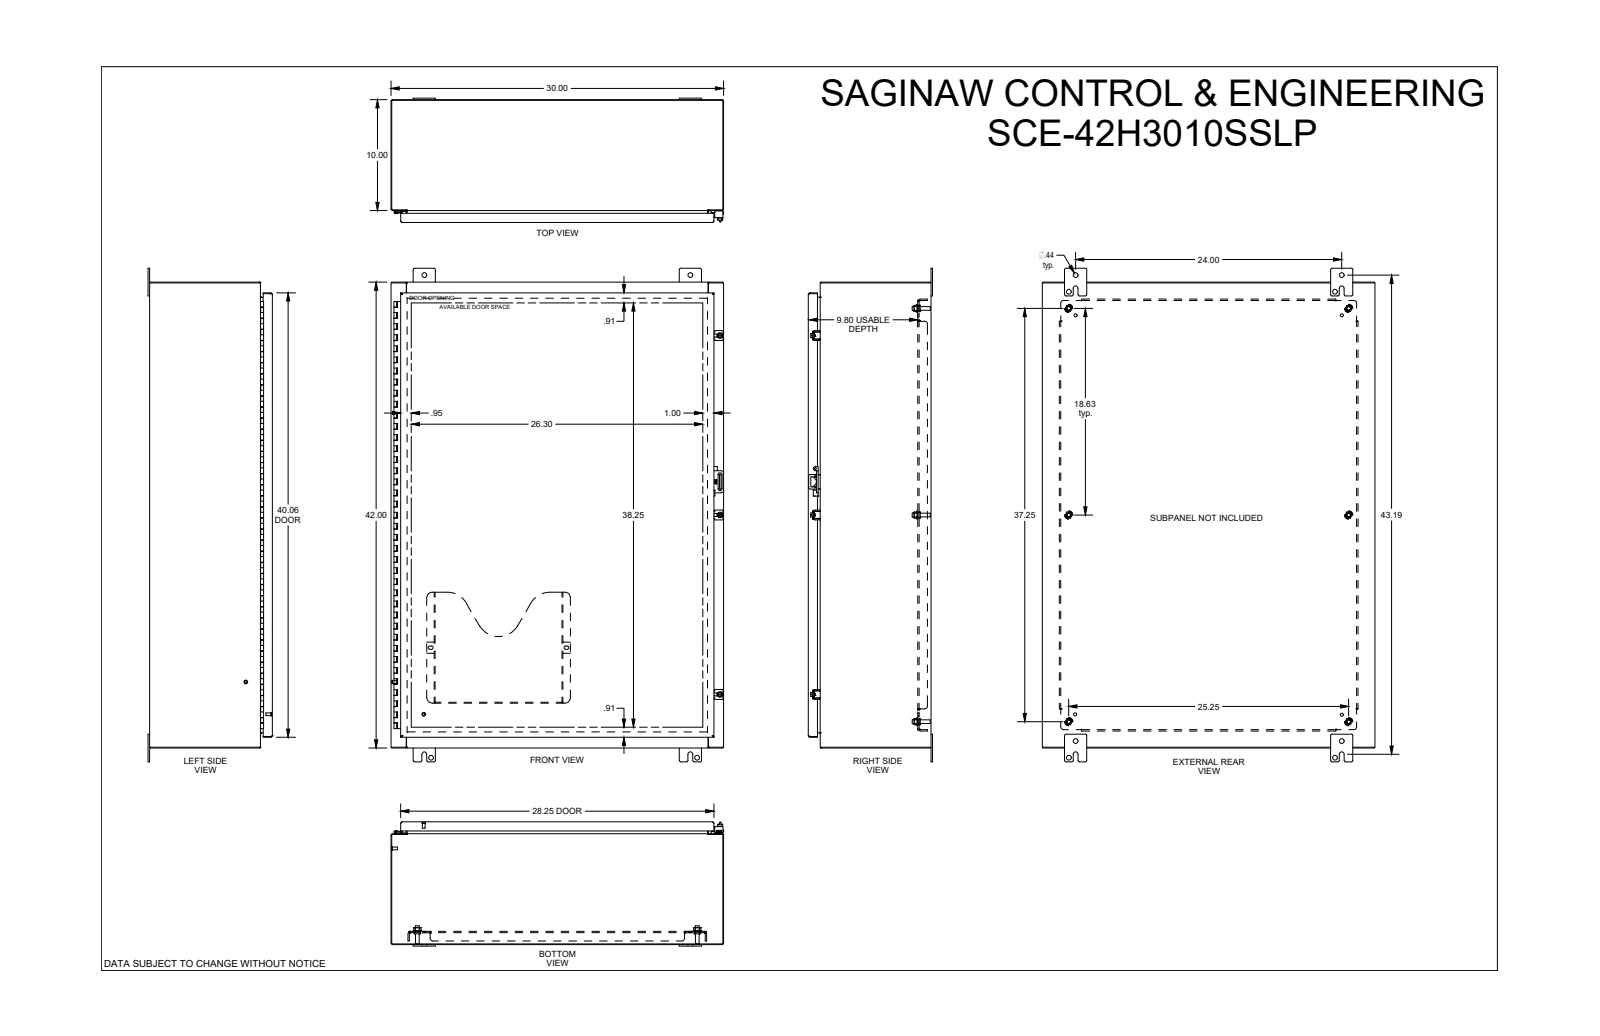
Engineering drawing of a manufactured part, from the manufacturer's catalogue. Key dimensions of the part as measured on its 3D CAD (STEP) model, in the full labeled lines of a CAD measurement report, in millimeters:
Part name (STEP PRODUCT): SCE-42H3010SSLP
STEP written by: SolidWorks 2019 (CONFIG_CONTROL_DESIGN)
Units: millimetres
Bodies: 0 solids, 4158 faces (1720 planar, 880 cylindrical, 1558 other)
Overall size (bounding box): 1130.3 × 762 × 284.7
Round holes (diameter × count): ⌀11.1 ×8, ⌀4.8 ×6, ⌀4.9 ×6, ⌀6.4 ×6, ⌀9.3 ×6, ⌀12.7 ×6, ⌀7.1 ×4, ⌀5.2 ×3, ⌀4.1 ×2, ⌀3.3 ×1, ⌀3.4 ×1
Round bosses / shafts (diameter × count): ⌀6.3 ×8, ⌀14.3 ×6, ⌀9.3 ×6, ⌀8.4 ×6, ⌀6.5 ×6, ⌀4.8 ×6, ⌀6.4 ×4, ⌀12.9 ×3
Partial cylindrical surfaces — rounded edges, fillets, slot ends (radius × count): R0.3 ×166, R0.4 ×40, R0.7 ×36, R1.5 ×29, R0.8 ×27, R3.2 ×27, R1 ×22, R1.8 ×14
Main face-to-face distances: 1.9, 1.9, 279.3, 277.4, 30.5, 250.8, 281.3, 279.3, 252, 28.6
Hole centre spacings: 190.5, 381, 609.6, 13.1, 457.6, 571.5, 775, 41.1
